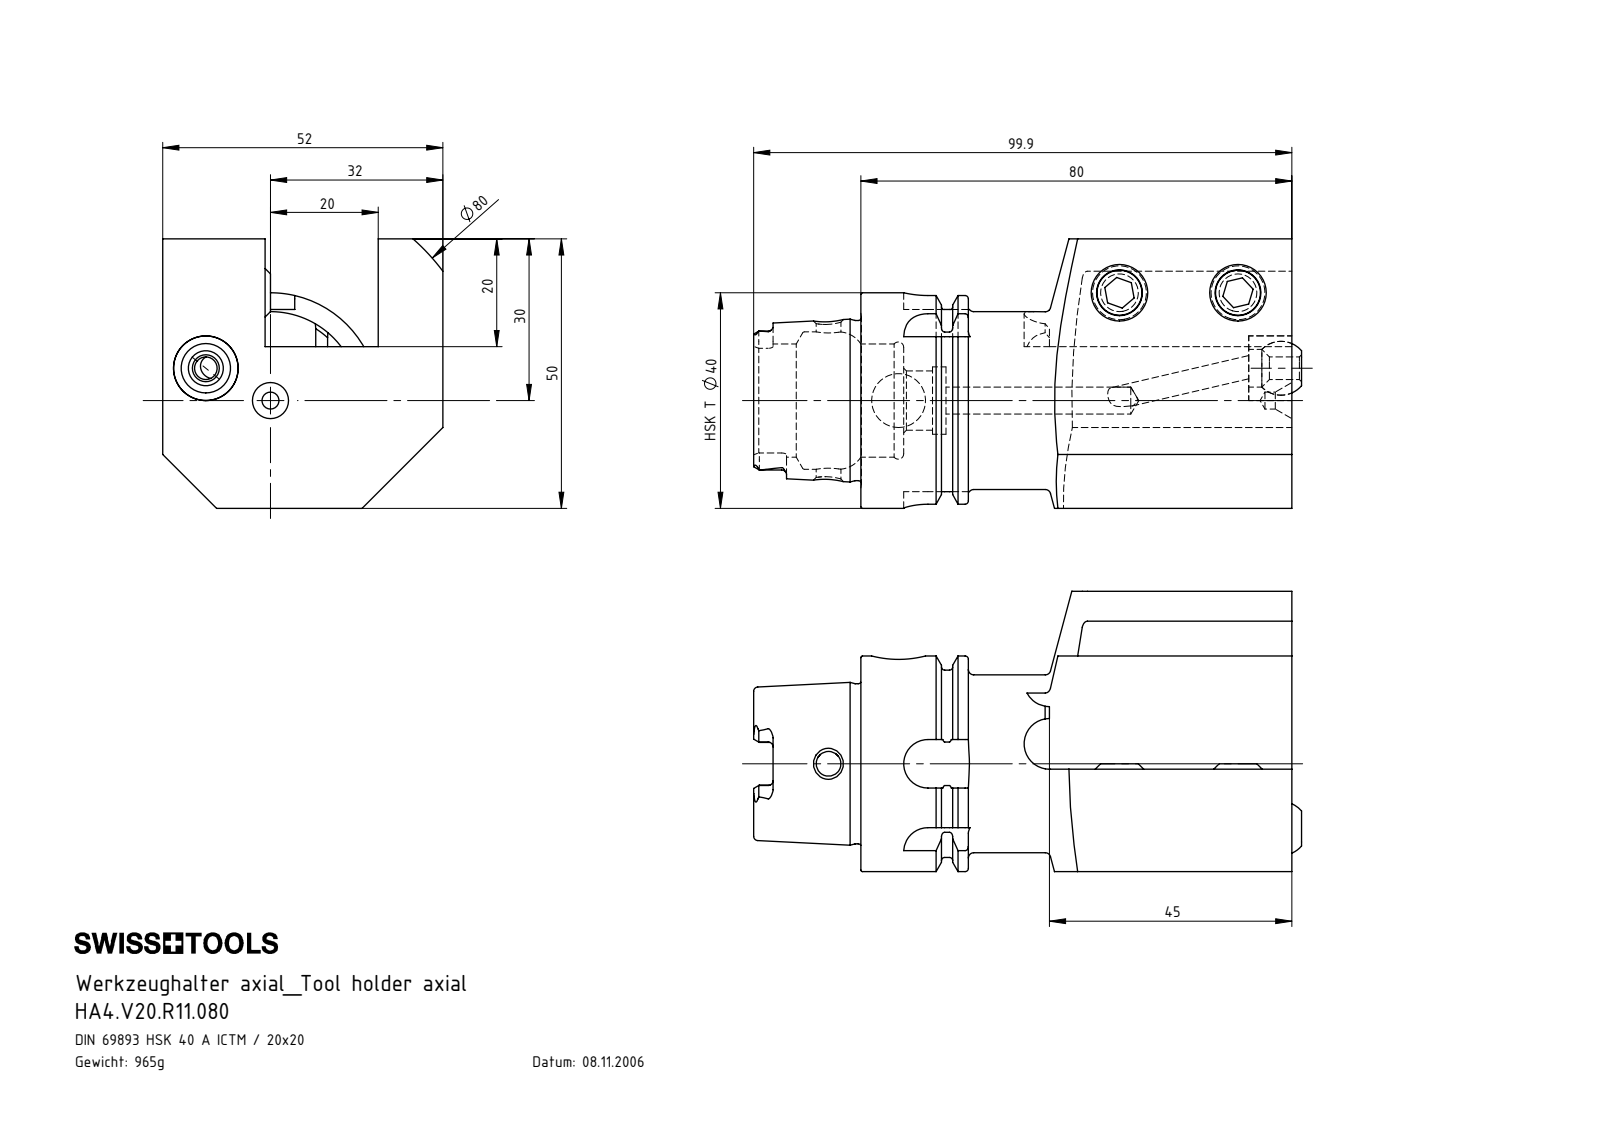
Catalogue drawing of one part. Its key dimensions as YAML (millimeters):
part_name: "KU1-U12.001.010_2; HA4.V20.R11.080; HA4-V20.R11.080_A_Fertigbearbeitung; KU1-U12.001.010_1 (+2 more)"
step_written_by: "SolidWorks 2017 (AUTOMOTIVE_DESIGN)"
units: millimeters
bodies: {solids: 5, faces: 185, planar: 79, cylindrical: 45, other: 61}
overall_size: [101.7, 52, 50]
volume: 123293
surface_area: 27586
round_holes:
  - {diameter: 4.2, count: 2}
  - {diameter: 8.5, count: 2}
  - {diameter: 3.15, count: 1}
  - {diameter: 4.6, count: 1}
  - {diameter: 5, count: 1}
  - {diameter: 7, count: 1}
  - {diameter: 10, count: 1}
  - {diameter: 11, count: 1}
  - {diameter: 12, count: 1}
  - {diameter: 12.5, count: 1}
  - {diameter: 21, count: 1}
  - {diameter: 25.5, count: 1}
round_bosses_or_shafts:
  - {diameter: 10, count: 2}
  - {diameter: 40, count: 1}
  - {diameter: 34.75, count: 1}
  - {diameter: 33, count: 1}
  - {diameter: 29.71, count: 1}
partial_cylinders:
  - {radius: 0.9, count: 6}
  - {radius: 1.88, count: 4}
  - {radius: 4.5, count: 4}
  - {radius: 4.7, count: 2}
  - {radius: 40, count: 1}
face_to_face_distances: [52, 20, 50, 12, 30, 40, 33, 21, 19, 80]
hole_center_spacings: [13.42, 22, 45.62, 66.1]
